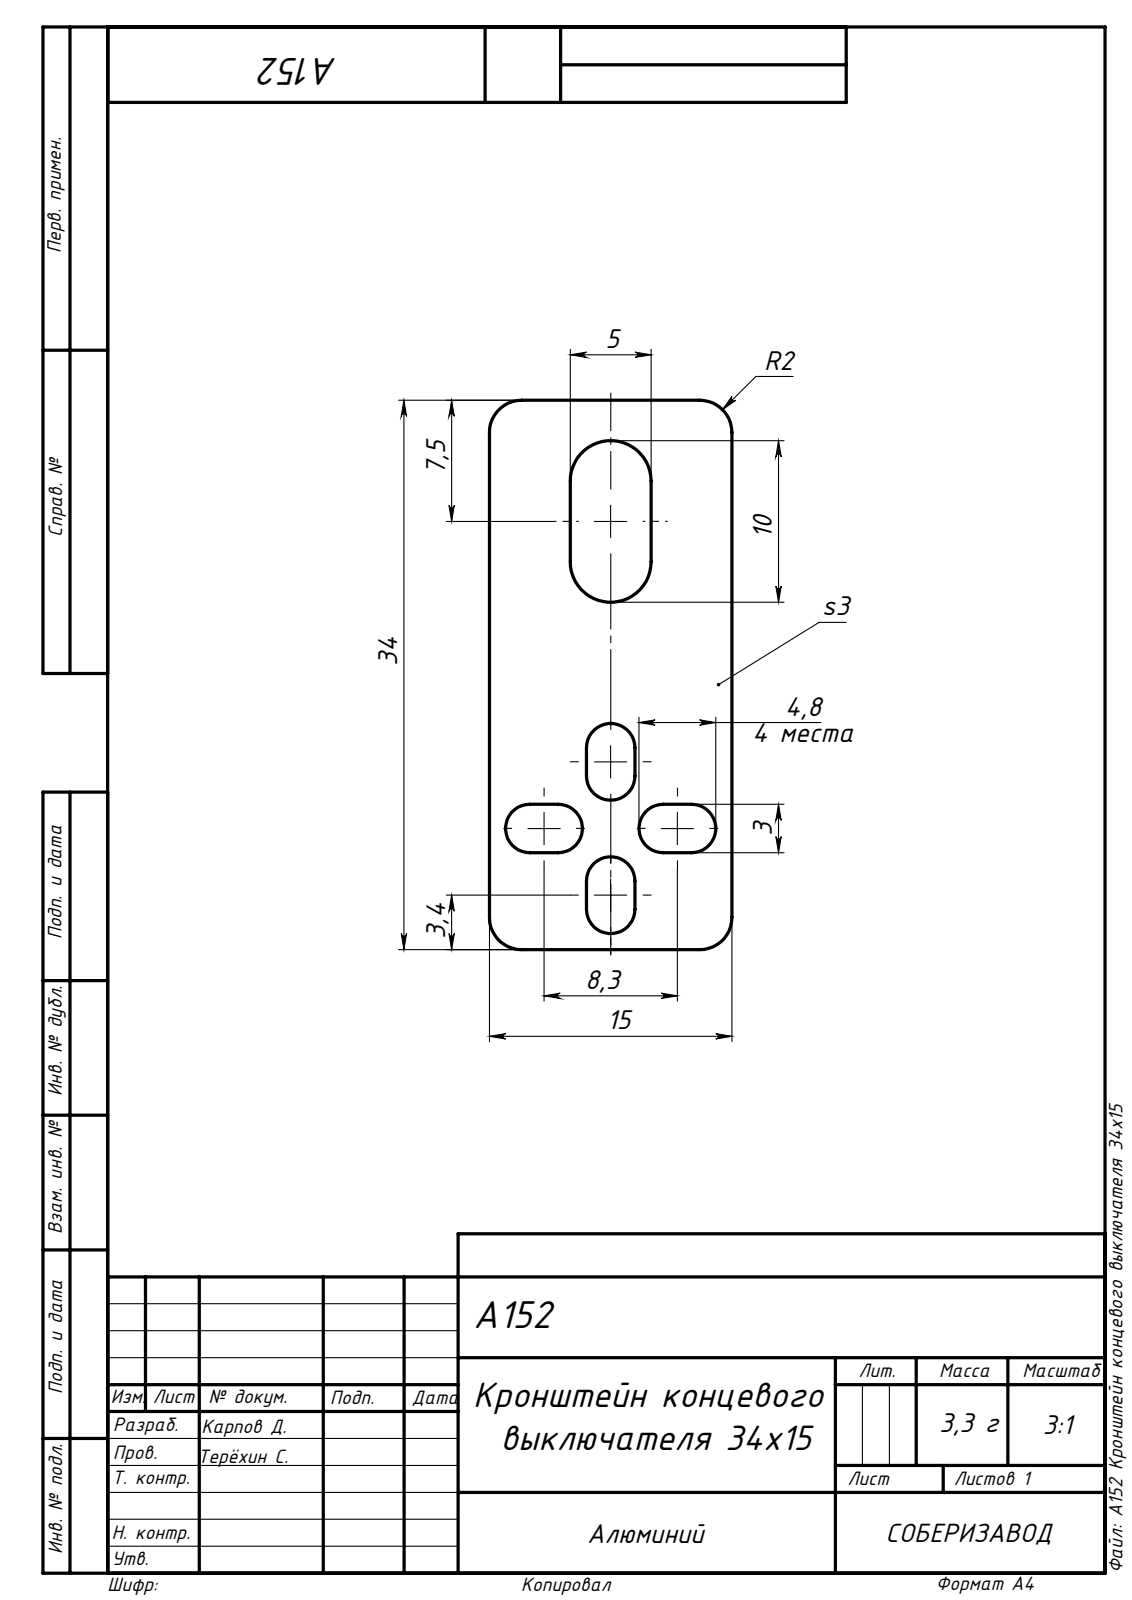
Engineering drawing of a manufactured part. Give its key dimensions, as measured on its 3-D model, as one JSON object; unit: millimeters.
{"part_name": "A152 Кронштейн концевого выключателя 34х15", "step_written_by": "SolidWorks 2018 (AUTOMOTIVE_DESIGN)", "units": "millimeters", "bodies": {"solids": 1, "faces": 32, "planar": 16, "cylindrical": 16, "other": 0}, "overall_size": [34, 15, 3], "volume_mm3": 1238, "surface_area_mm2": 1341, "partial_cylinders_radius": [[1.5, 8], [2, 4], [2.5, 2]], "face_to_face_distances": [3, 15, 5, 34, 9, 6, 10, 1, 4, 25]}
